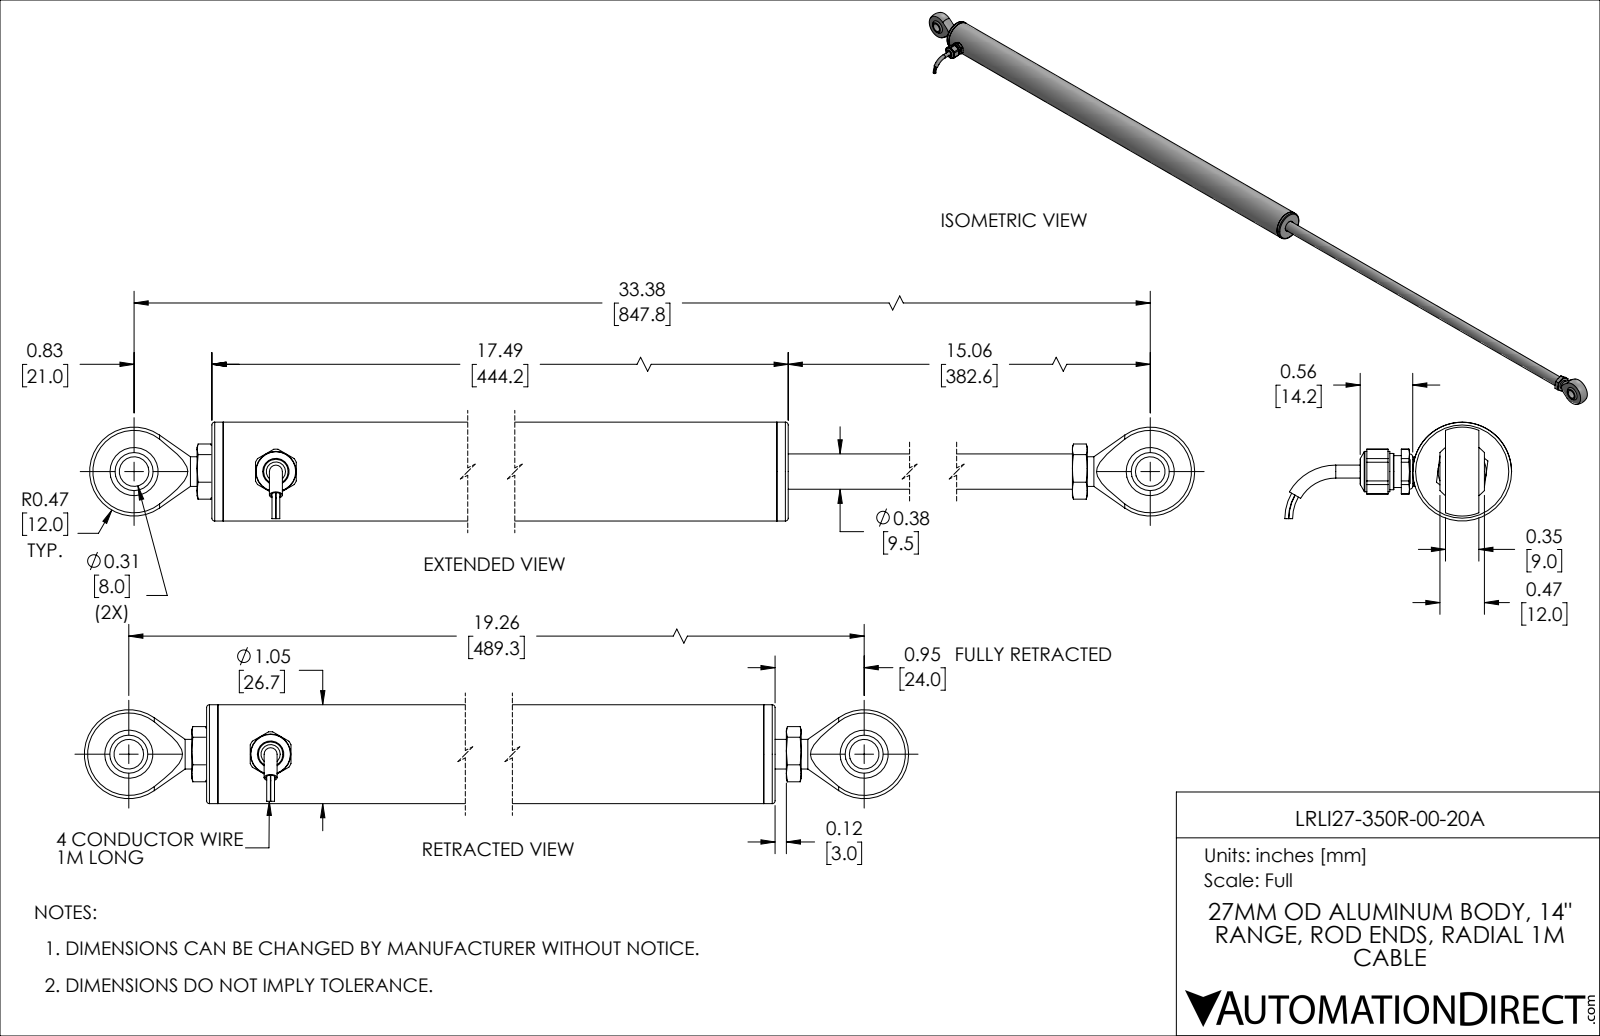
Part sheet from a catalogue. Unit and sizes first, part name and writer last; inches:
Units: inches
Overall size (bounding box): 20.088 × 2.409 × 1.05
Round holes (diameter × count): ⌀0.268 ×2, ⌀0.315 ×2, ⌀0.106 ×1, ⌀0.138 ×1, ⌀0.156 ×1, ⌀0.187 ×1, ⌀0.201 ×1, ⌀0.205 ×1, ⌀0.272 ×1, ⌀0.275 ×1, ⌀0.313 ×1, ⌀0.36 ×1
Round bosses / shafts (diameter × count): ⌀0.039 ×4, ⌀0.315 ×2, ⌀1.05 ×1, ⌀0.85 ×1, ⌀0.848 ×1, ⌀0.685 ×1, ⌀0.625 ×1, ⌀0.5 ×1
Partial cylindrical surfaces — rounded edges, fillets, slot ends (radius × count): R0.01 ×2, R0.067 ×2, R0.25 ×2, R0.197 ×1, R0.224 ×1, R0.238 ×1, R0.344 ×1, R0.407 ×1
Main face-to-face distances: 0.354, 17.49, 0.737, 16.753, 0.12, 17.37, 0.5, 1.65, 0.913, 15.84
Hole centre spacings: 1.507, 17.637, 19.144
Volume: 8.877 in³ · Surface area: 181.3 in²
Bodies: 28 solids, 298 faces (114 planar, 92 cylindrical, 92 other)
Part name (STEP PRODUCT): LRLE27-350R-00-10A
STEP written by: SolidWorks 2019 (AUTOMOTIVE_DESIGN)
